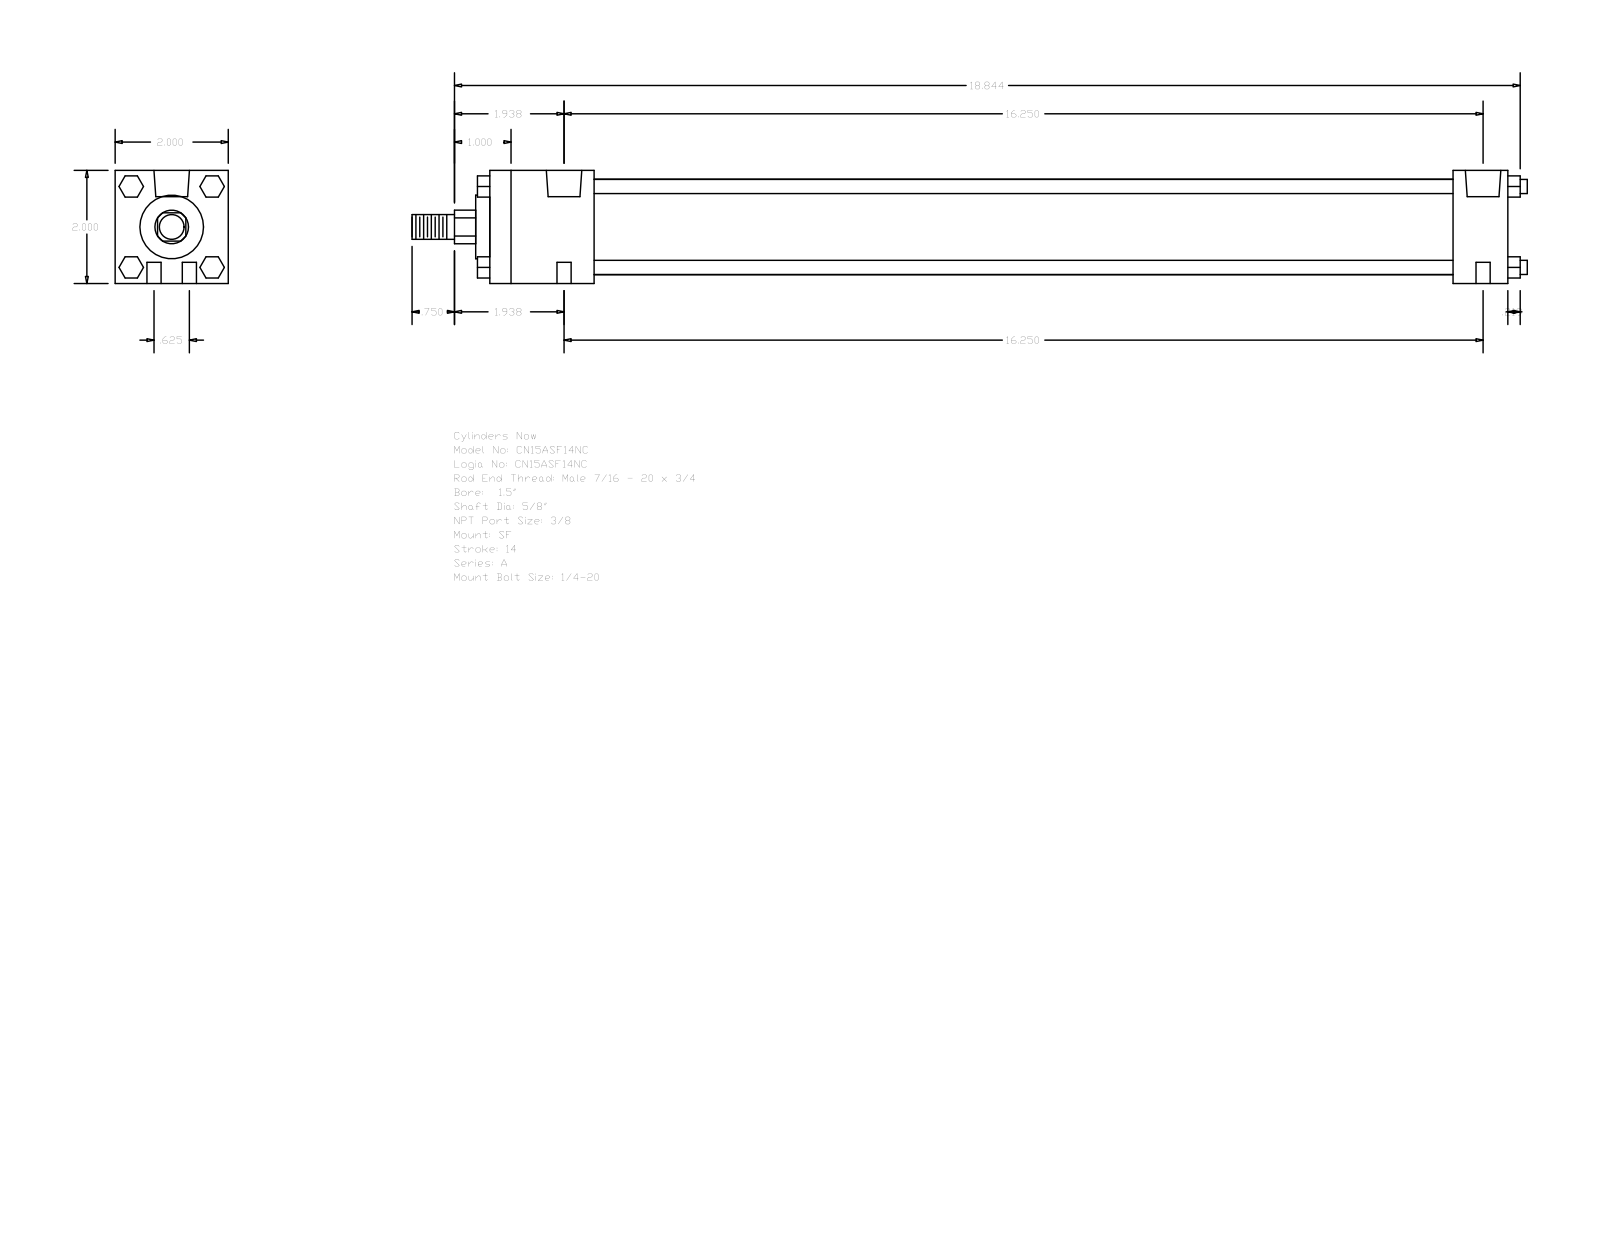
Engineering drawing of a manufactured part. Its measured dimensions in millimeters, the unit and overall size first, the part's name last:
Units: millimetres
Overall size (bounding box): 500.86 × 50.8 × 50.8
Round holes (diameter × count): ⌀6.35 ×4, ⌀5.56 ×2, ⌀15.93 ×2
Round bosses / shafts (diameter × count): ⌀6.35 ×4, ⌀42.93 ×1, ⌀28.57 ×1, ⌀15.88 ×1, ⌀11.11 ×1
Partial cylindrical surfaces — rounded edges, fillets, slot ends (radius × count): R7.54 ×1
Main face-to-face distances: 50.8, 457.19, 46.83, 432.59, 385.76, 410.36, 24.6, 6.35, 9.52, 53.18
Hole centre spacings: 7.94, 412.83, 412.75, 15.88, 413.06, 404.81
Bodies: 0 solids, 124 faces (94 planar, 30 cylindrical, 0 other)
Part name (STEP PRODUCT): A_SF__0150_0.625
STEP written by: GSSL Pune (CONFIG_CONTROL_DESIGN)
